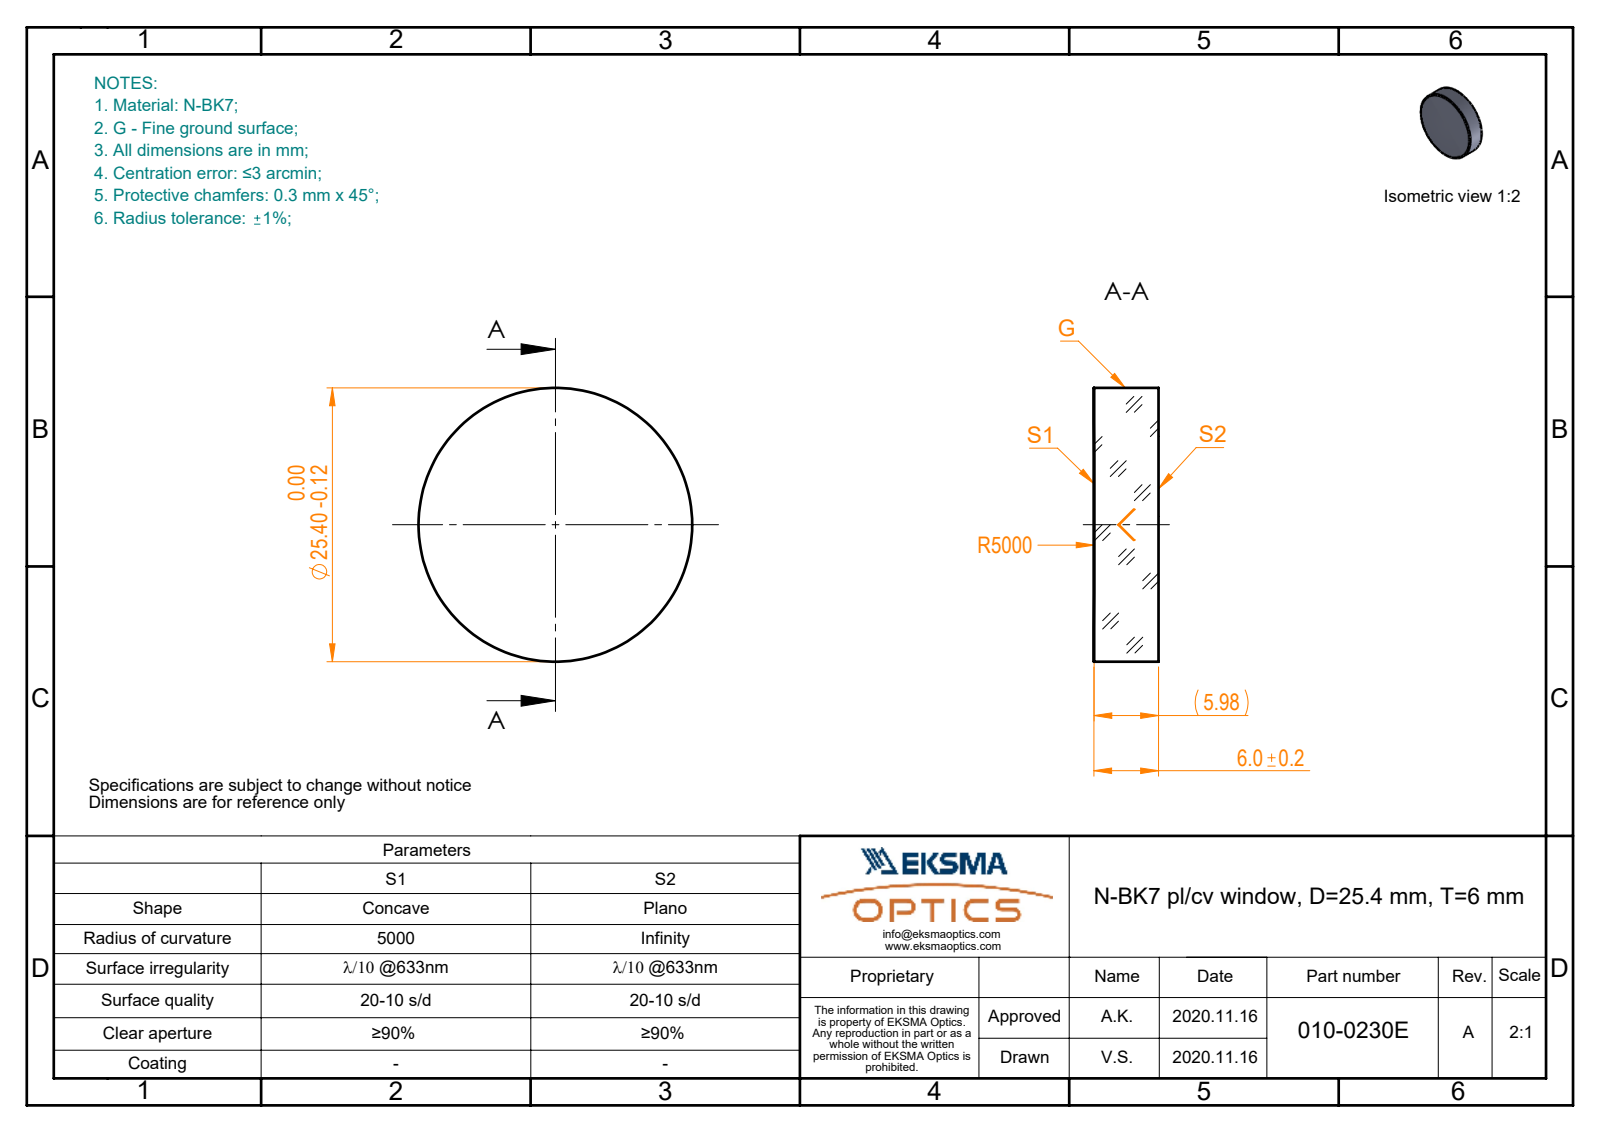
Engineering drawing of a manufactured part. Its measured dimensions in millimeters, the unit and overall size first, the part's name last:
Units: millimetres
Overall size (bounding box): 25.4 × 25.4 × 6
Round bosses / shafts (diameter × count): ⌀25.4 ×1
Volume: 3 036 mm³ · Surface area: 1 492 mm²
Bodies: 1 solid, 5 faces (1 planar, 2 cylindrical, 2 other)
Part name (STEP PRODUCT): 010-0230E_N-BK7_PCV_window
STEP written by: SolidWorks 2019 (CONFIG_CONTROL_DESIGN)
